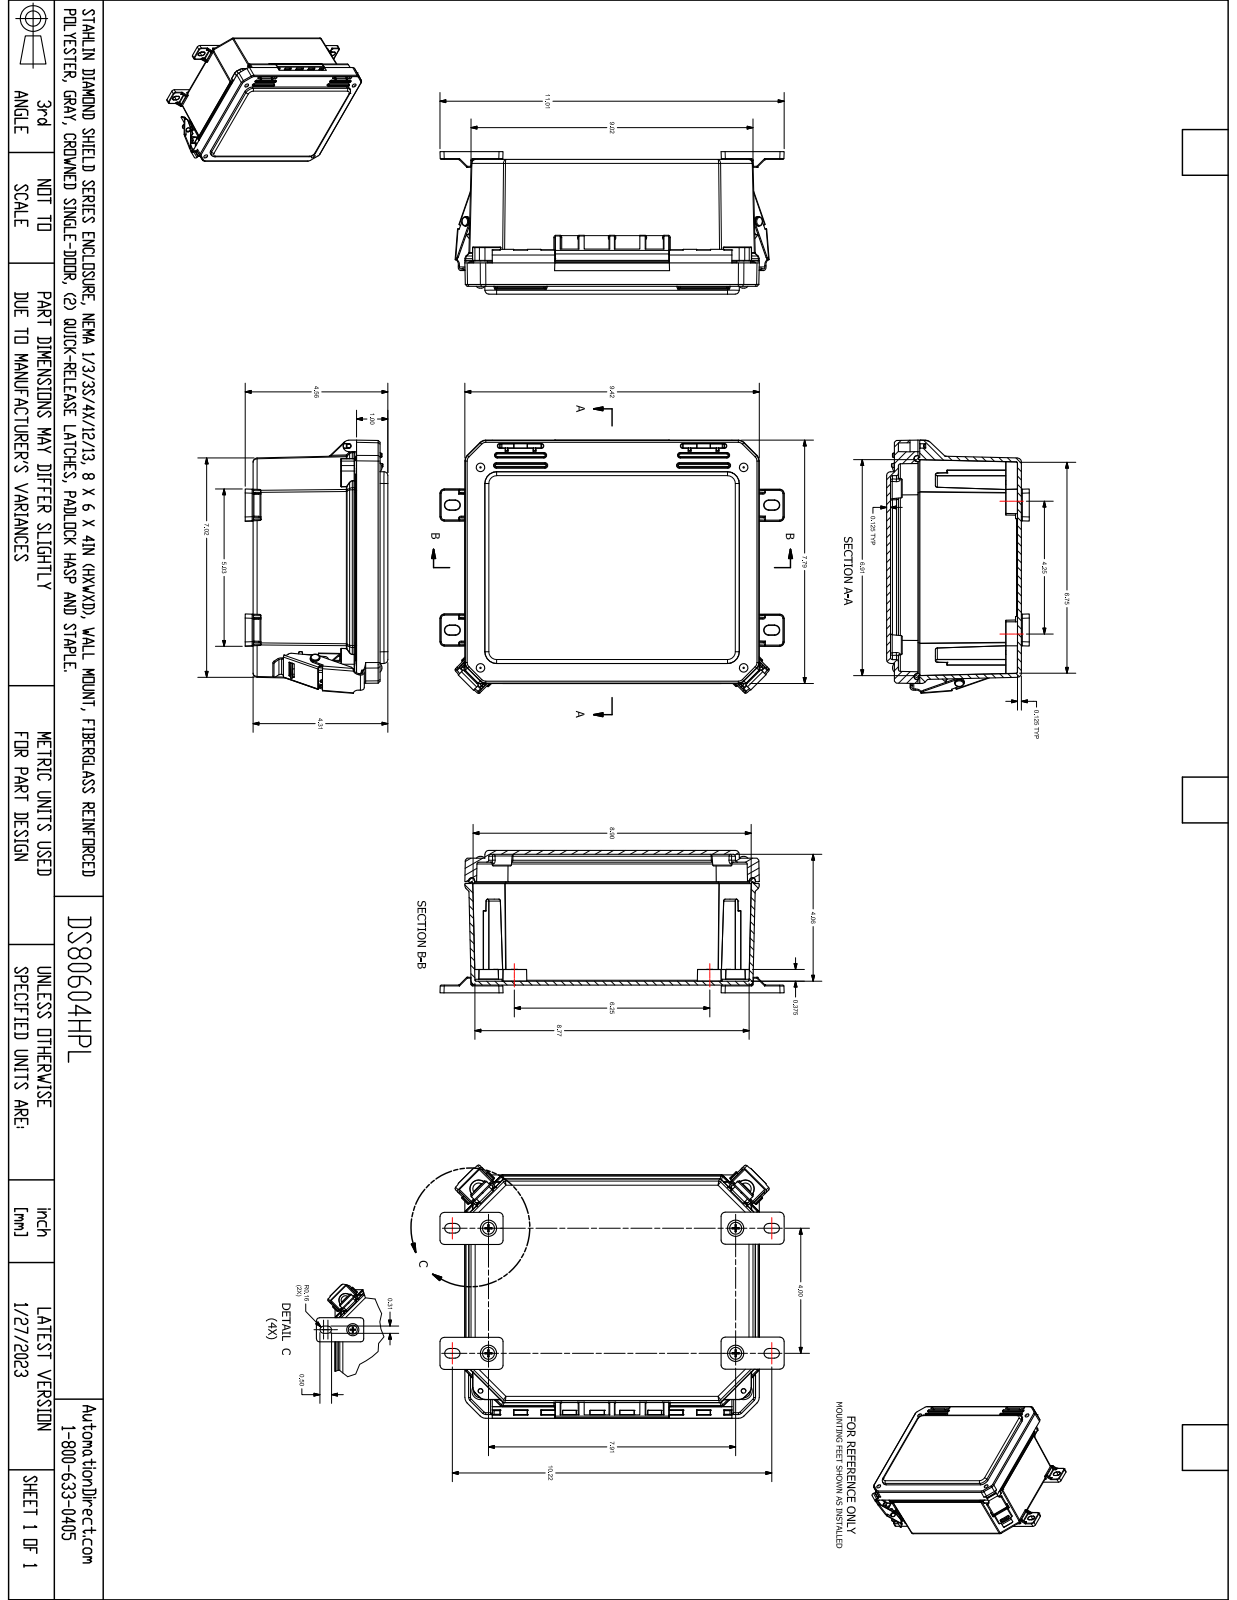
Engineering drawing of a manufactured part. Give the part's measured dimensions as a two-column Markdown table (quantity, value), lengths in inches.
| quantity | value |
| --- | --- |
| part name | FR80604HPL |
| STEP written by | SolidWorks 2021 (AUTOMOTIVE_DESIGN) |
| units | inches |
| bodies | 29 solids, 2341 faces (749 planar, 995 cylindrical, 597 other) |
| overall size | 10.045 × 8.104 × 4.529 |
| volume | 44.83 in³ |
| surface area | 628.1 in² |
| round holes (diameter × count) | 0.152 × 8, 0.159 × 8, 0.135 × 7, 0.135 × 5, 0.15 × 4, 0.156 × 4, 0.252 × 4, 0.253 × 4, 0.137 × 3, 0.219 × 2, 0.227 × 2, 0.313 × 2 |
| round bosses / shafts (diameter × count) | 0.27 × 8, 0.87 × 4, 0.3 × 4, 0.262 × 4, 0.209 × 4, 0.135 × 4, 0.435 × 2 |
| partial cylindrical surfaces (radius × count) | 0.01 × 120, 0.005 × 94, 0.02 × 77, 0.03 × 71, 0.06 × 34, 0.09 × 26, 0.03 × 24, 0.096 × 24 |
| main face-to-face distances | 0.125, 0.125, 4.059, 4.184, 4.309, 4.184, 0.25, 3.934, 0.124, 0.375 |
| hole center spacings | 8.415, 7.411, 8.414, 6.413, 9.065, 7.767, 8.249, 6.415 |
